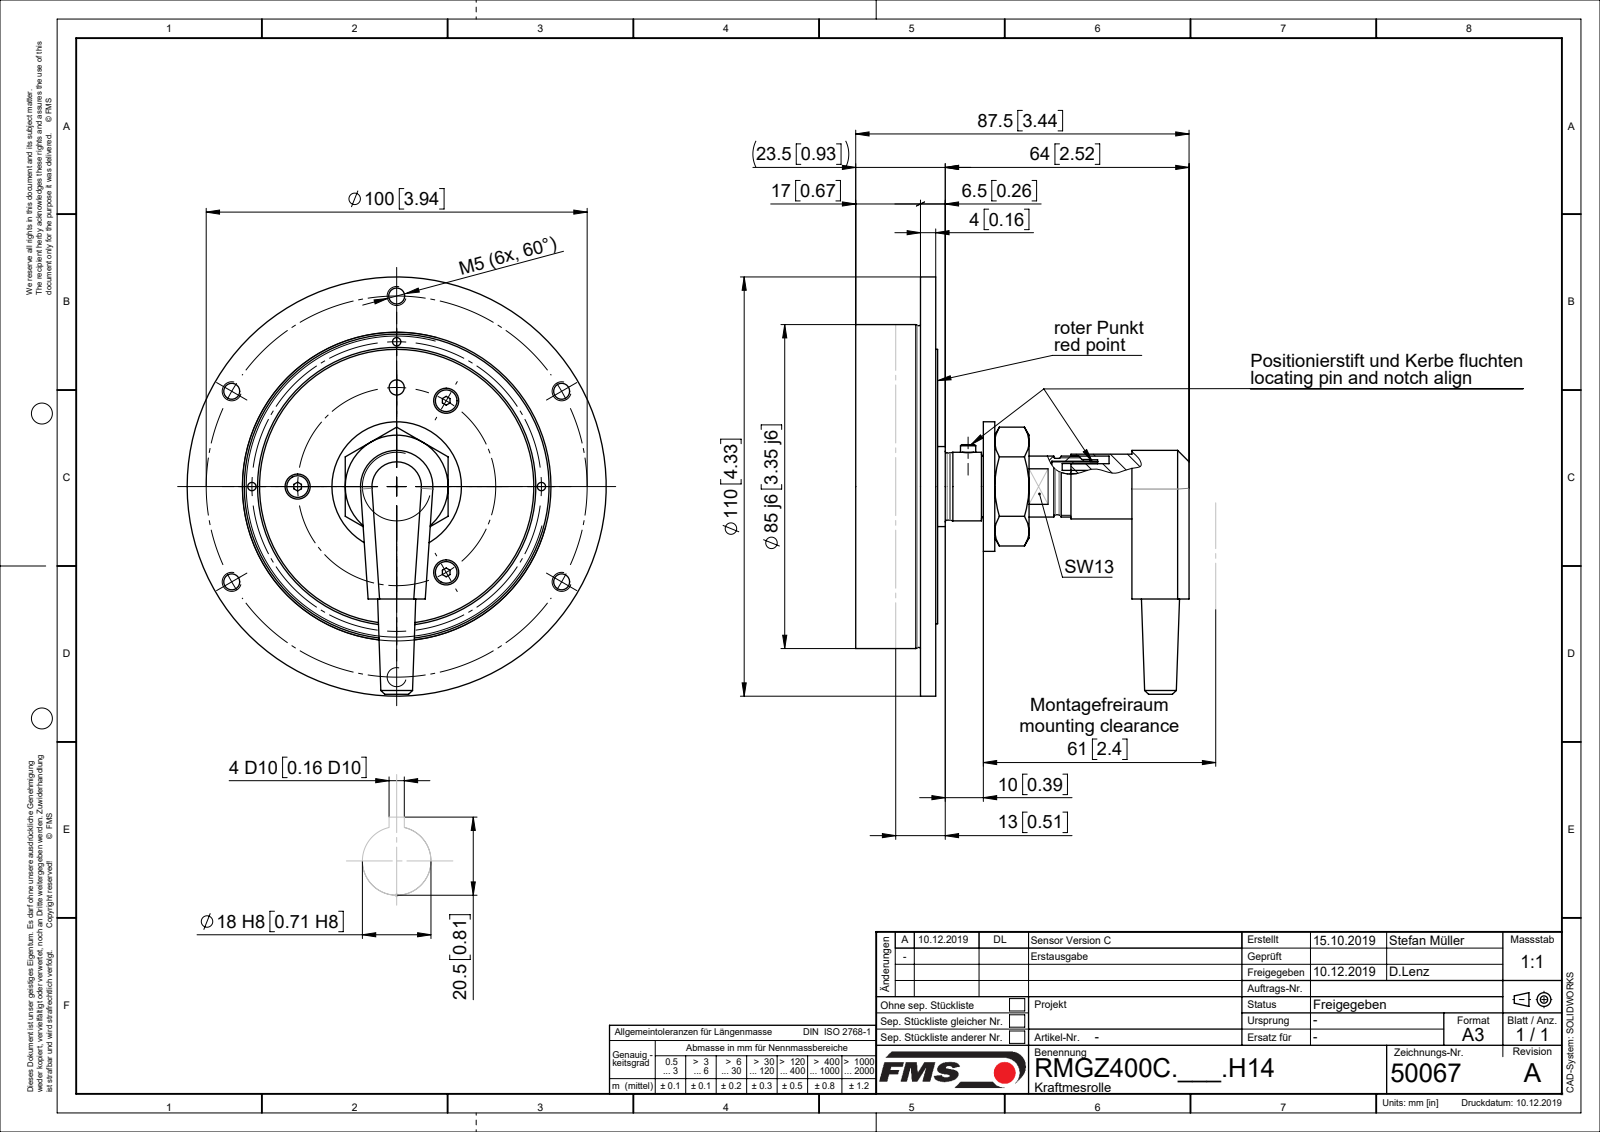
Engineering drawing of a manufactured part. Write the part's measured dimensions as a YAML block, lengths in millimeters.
part_name: "R50067; R4941504; TEIL1; R47407 (+8 more)"
step_written_by: "Mechanical Desktop 2007 (CONFIG_CONTROL_DESIGN)"
units: millimeters
bodies: {solids: 9, faces: 266, planar: 66, cylindrical: 129, other: 71}
overall_size: [110, 110, 87.5]
volume: 147285
surface_area: 77843
round_holes:
  - {diameter: 4.33, count: 6}
  - {diameter: 2, count: 5}
  - {diameter: 2.2, count: 4}
  - {diameter: 2.3, count: 3}
  - {diameter: 3.4, count: 3}
  - {diameter: 3, count: 1}
  - {diameter: 4, count: 1}
  - {diameter: 10, count: 1}
  - {diameter: 11.5, count: 1}
  - {diameter: 13.3, count: 1}
  - {diameter: 16.68, count: 1}
  - {diameter: 19, count: 1}
round_bosses_or_shafts:
  - {diameter: 110, count: 1}
  - {diameter: 85, count: 1}
  - {diameter: 80, count: 1}
  - {diameter: 72, count: 1}
  - {diameter: 66, count: 1}
  - {diameter: 63, count: 1}
  - {diameter: 34, count: 1}
  - {diameter: 21, count: 1}
face_to_face_distances: [0.5, 4, 5.5, 15.5, 17.5, 12, 1, 21, 2, 3.5]
hole_center_spacings: [50, 30.4, 86.6, 12, 25.56, 26, 38, 45.21]
